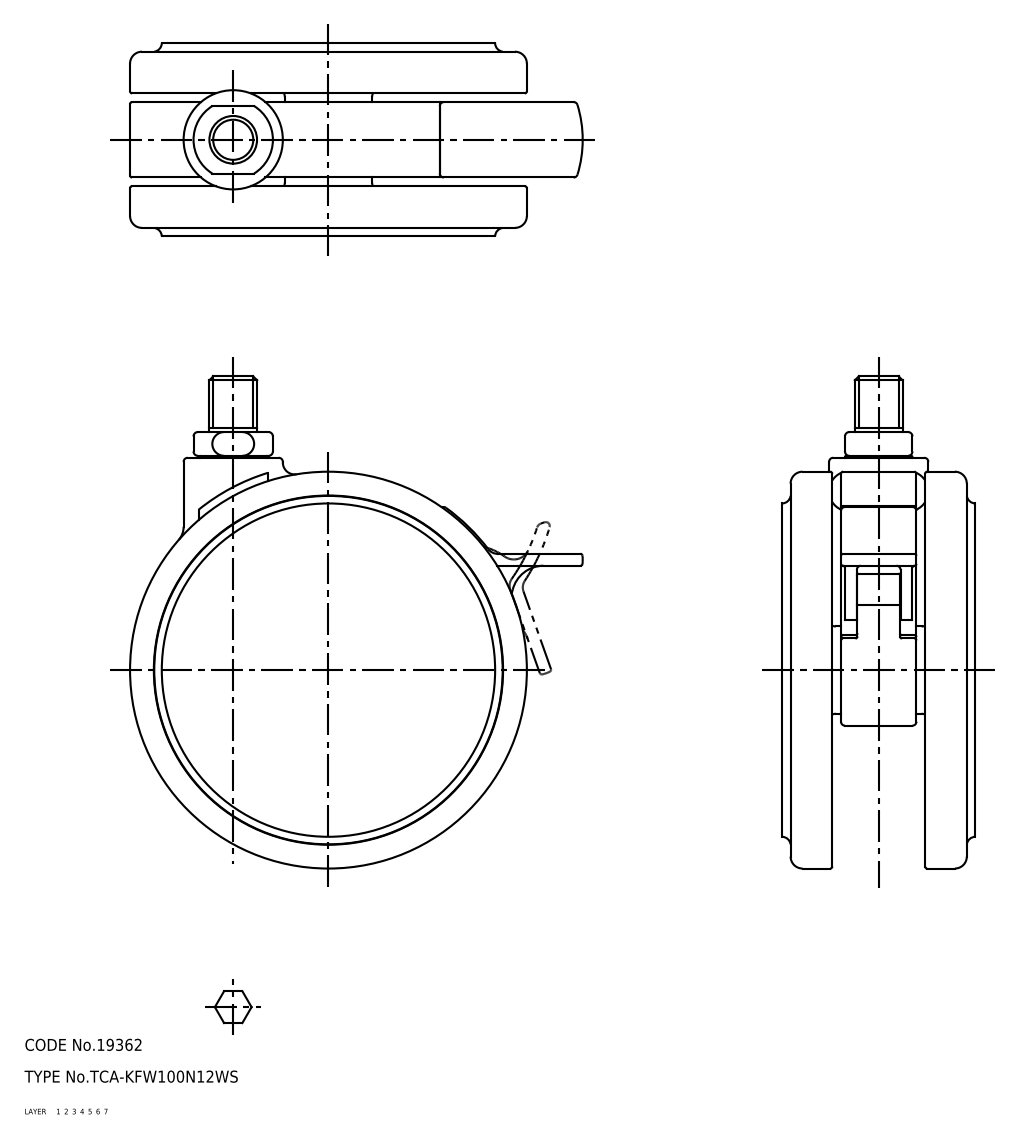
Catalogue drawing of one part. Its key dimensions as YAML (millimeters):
part_name: "TCA-KFW100N12WS; caster"
step_written_by: "SolidWorks 2015 (AUTOMOTIVE_DESIGN)"
units: millimeters
bodies: {solids: 1, faces: 1520, planar: 528, cylindrical: 654, other: 338}
overall_size: [124, 114.07, 48.6]
volume: 185560
surface_area: 95672
round_holes:
  - {diameter: 2.4, count: 1}
  - {diameter: 3, count: 1}
  - {diameter: 3.3, count: 1}
  - {diameter: 3.6, count: 1}
  - {diameter: 5.8, count: 1}
  - {diameter: 6.1, count: 1}
  - {diameter: 8.07, count: 1}
  - {diameter: 9, count: 1}
  - {diameter: 9.3, count: 1}
  - {diameter: 10.7, count: 1}
  - {diameter: 12.3, count: 1}
  - {diameter: 13, count: 1}
round_bosses_or_shafts:
  - {diameter: 100, count: 1}
  - {diameter: 87.8, count: 1}
  - {diameter: 25, count: 1}
  - {diameter: 22, count: 1}
  - {diameter: 20, count: 1}
  - {diameter: 17, count: 1}
  - {diameter: 12, count: 1}
  - {diameter: 10.5, count: 1}
partial_cylinders:
  - {radius: 0.5, count: 63}
  - {radius: 1, count: 61}
  - {radius: 1.5, count: 21}
  - {radius: 0.2, count: 18}
  - {radius: 0.3, count: 17}
  - {radius: 2, count: 16}
  - {radius: 3, count: 7}
  - {radius: 0.7, count: 2}
face_to_face_distances: [1.8, 45, 46.8, 3.6, 43.2, 12.6, 32.4, 9, 36, 10.8]
hole_center_spacings: [21.4, 29.97, 43.99]
